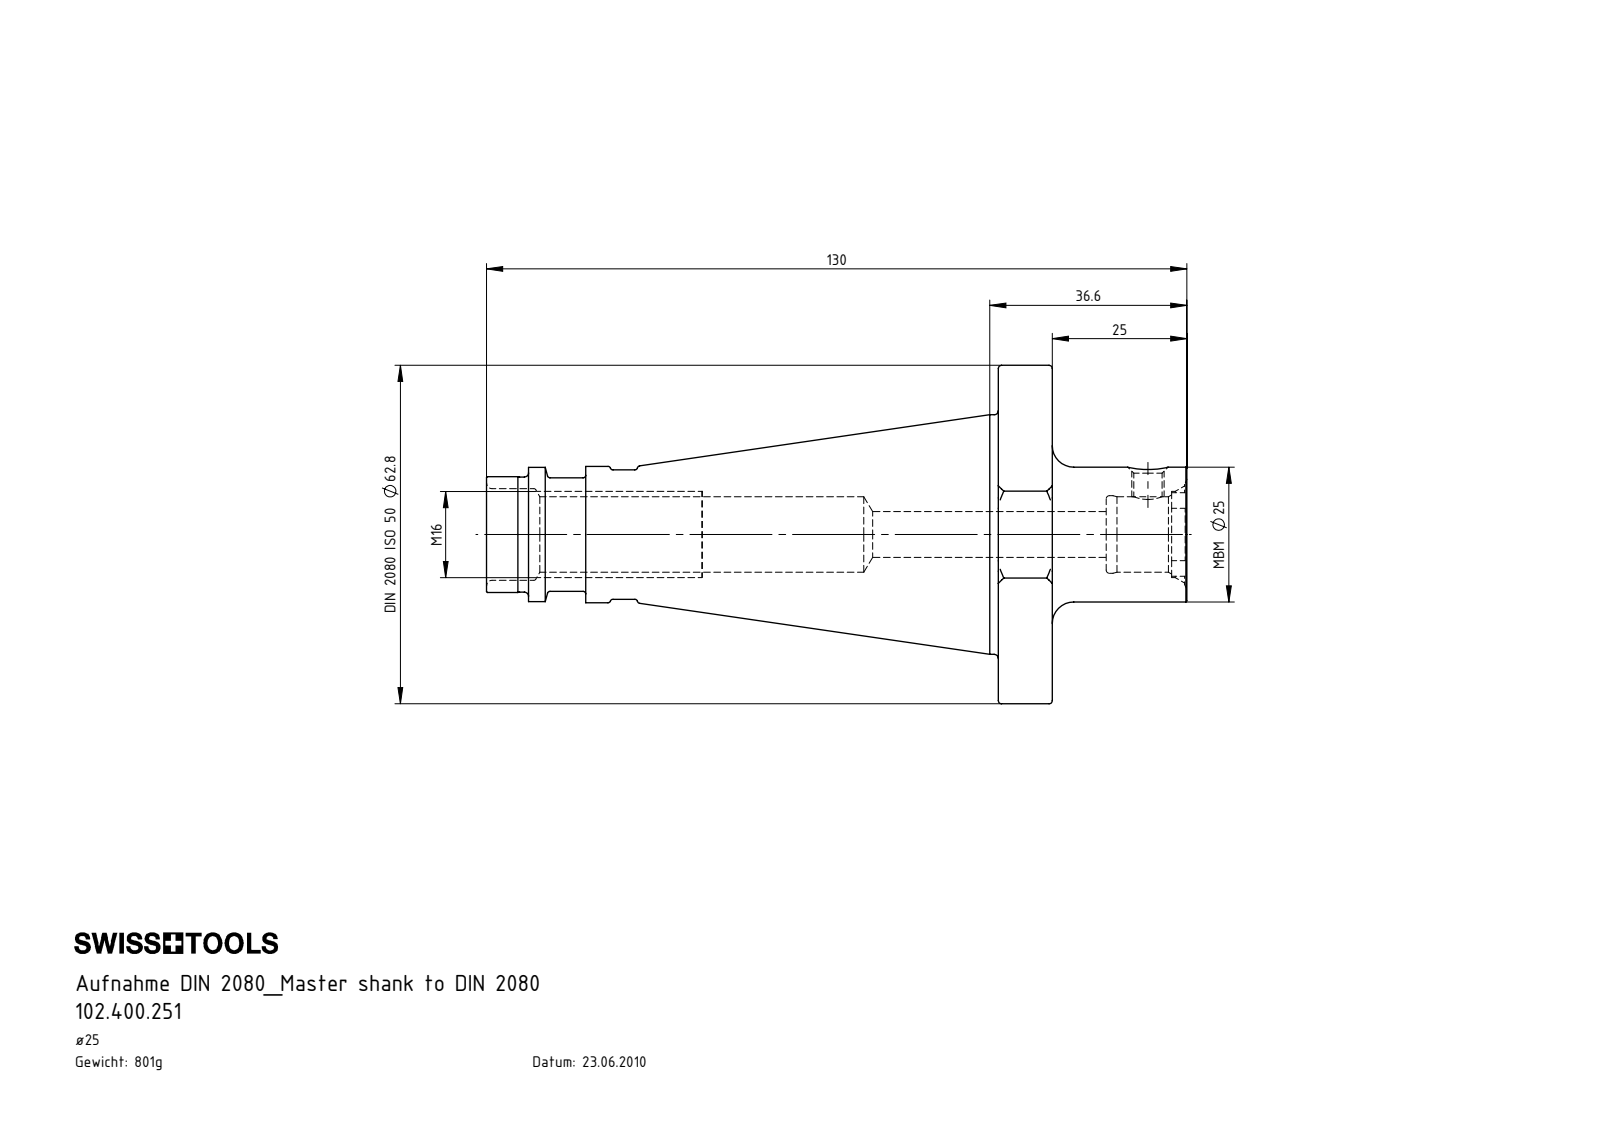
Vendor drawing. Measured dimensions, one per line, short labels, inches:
name: SZ4-MB2.K01.036
written by: SolidWorks 2017 (AUTOMOTIVE_DESIGN)
unit: in
bodies: 1 solid, 138 faces (31 planar, 53 cylindrical, 54 other)
size: 5.118 × 2.472 × 2.39
volume: 6.229 in³; area: 35.87 in²
holes: 1× ⌀0.207, 1× ⌀0.335, 1× ⌀0.551, 1× ⌀0.567, 1× ⌀0.669
bosses: 1× ⌀2.472, 1× ⌀1.75, 1× ⌀0.996, 1× ⌀0.984, 1× ⌀0.981, 1× ⌀0.945, 1× ⌀0.846, 1× ⌀0.841
rounds: 12× R0.063, 4× R0.106, 1× R0.315, 1× R0.375
face distances: 0.394, 1.378, 0.984, 1.772, 3.016, 3.409, 4.394, 0.634, 4.281, 1.266
